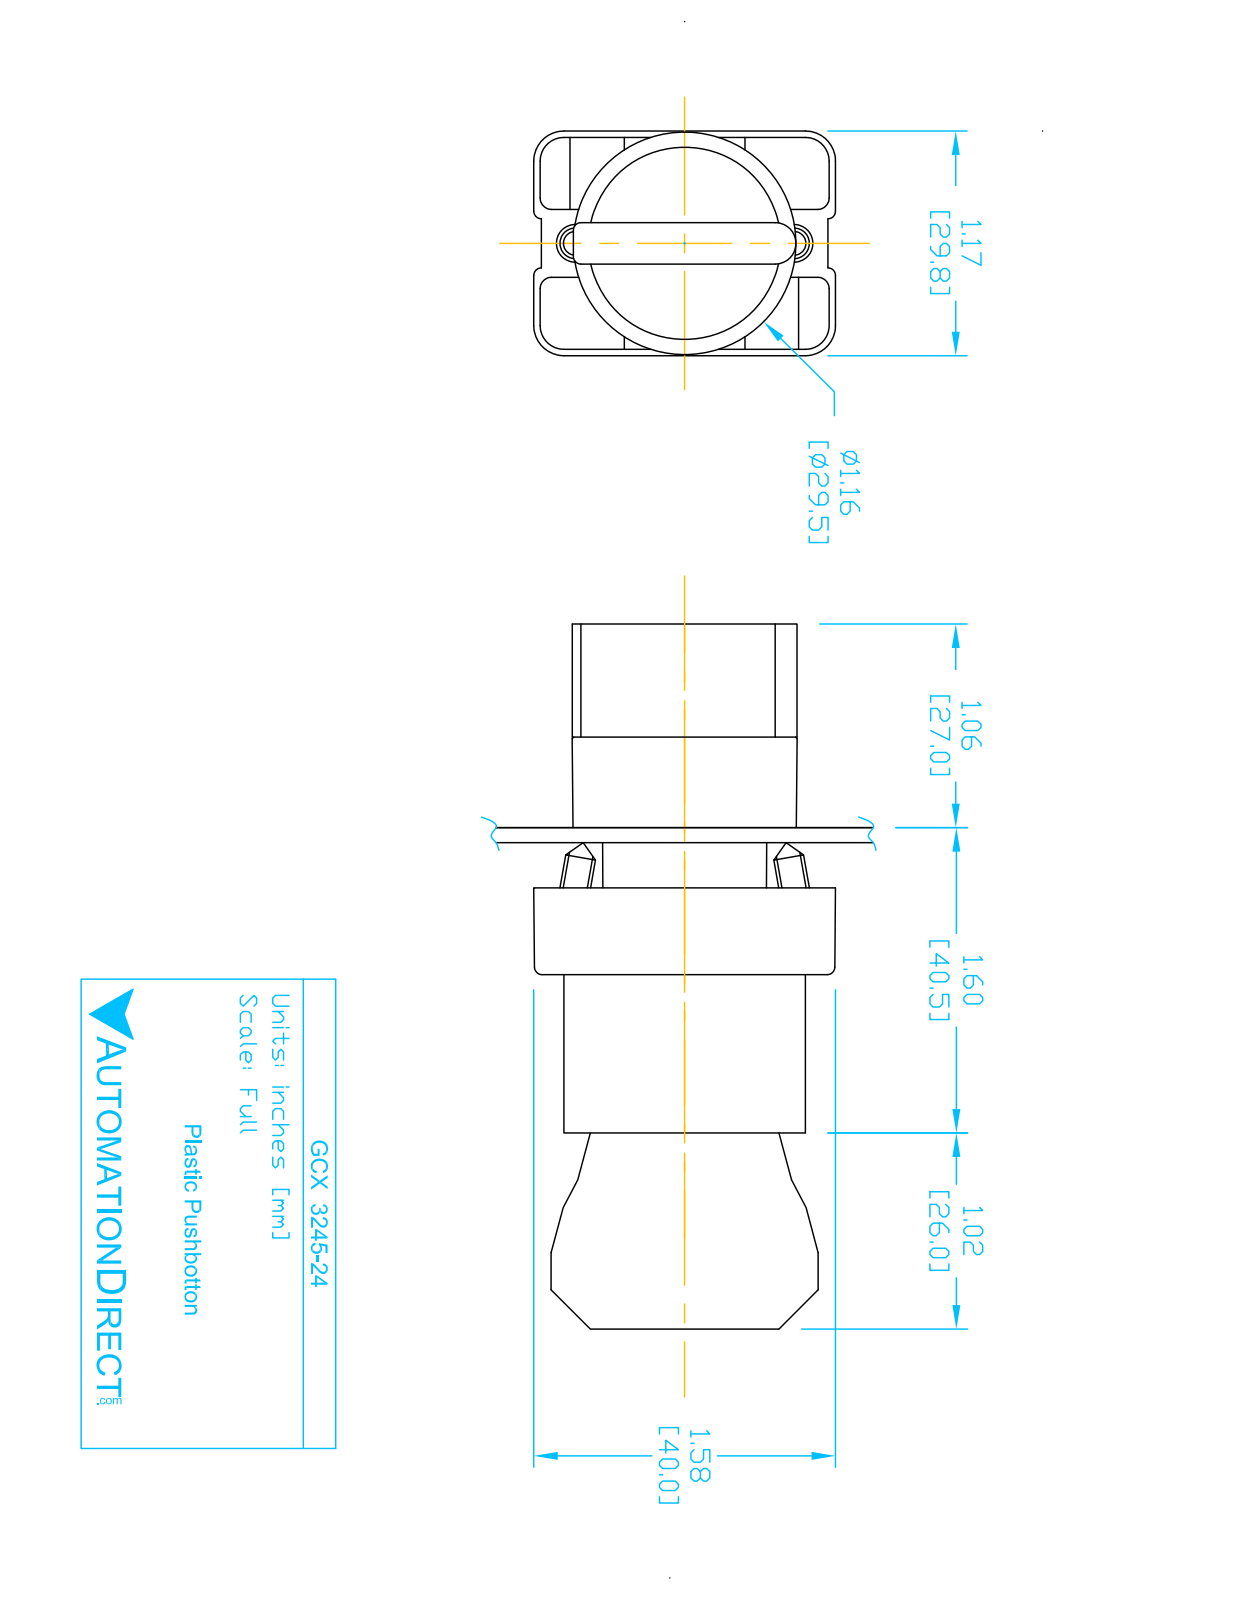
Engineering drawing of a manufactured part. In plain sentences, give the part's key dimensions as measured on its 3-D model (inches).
The part is named "GCX3245 OPERATOR; ecx1040; ECX3029-2; ECX1050 (+1 more)". Its 3-D file was written by "SolidWorks 2016 (AUTOMOTIVE_DESIGN)". It is 8 solids with 445 faces: 263 planar, 151 cylindrical and 31 other. Overall it measures 3.653 by 1.581 by 1.177 inches. Its volume is 2.799 cubic inches and its surface area 39 square inches. Round holes: 2 of diameter 0.079, 2 of diameter 0.124, 2 of diameter 0.13, 1 of diameter 0.087, 1 of diameter 0.197, 1 of diameter 0.469, 1 of diameter 0.878, 1 of diameter 0.888, 1 of diameter 1.024. Round bosses or shafts: 4 of diameter 0.157, 1 of diameter 1.175, 1 of diameter 1.004, 1 of diameter 0.945, 1 of diameter 0.856, 1 of diameter 0.78, 1 of diameter 0.504. Partial cylindrical surfaces (rounded edges, fillets, slot ends): 24 of radius 0.059, 12 of radius 0.041, 12 of radius 0.124, 12 of radius 0.157, 9 of radius 0.039, 2 of radius 0.128, 1 of radius 0.02, 1 of radius 0.063. The main face-to-face distances are 0.827, 2.02, 1.193, 0.579, 1.244, 1.171, 0.472, 0.469, 0.031, 0.033. The hole center spacings are 0.236, 0.544, 0.472, 0.49.
